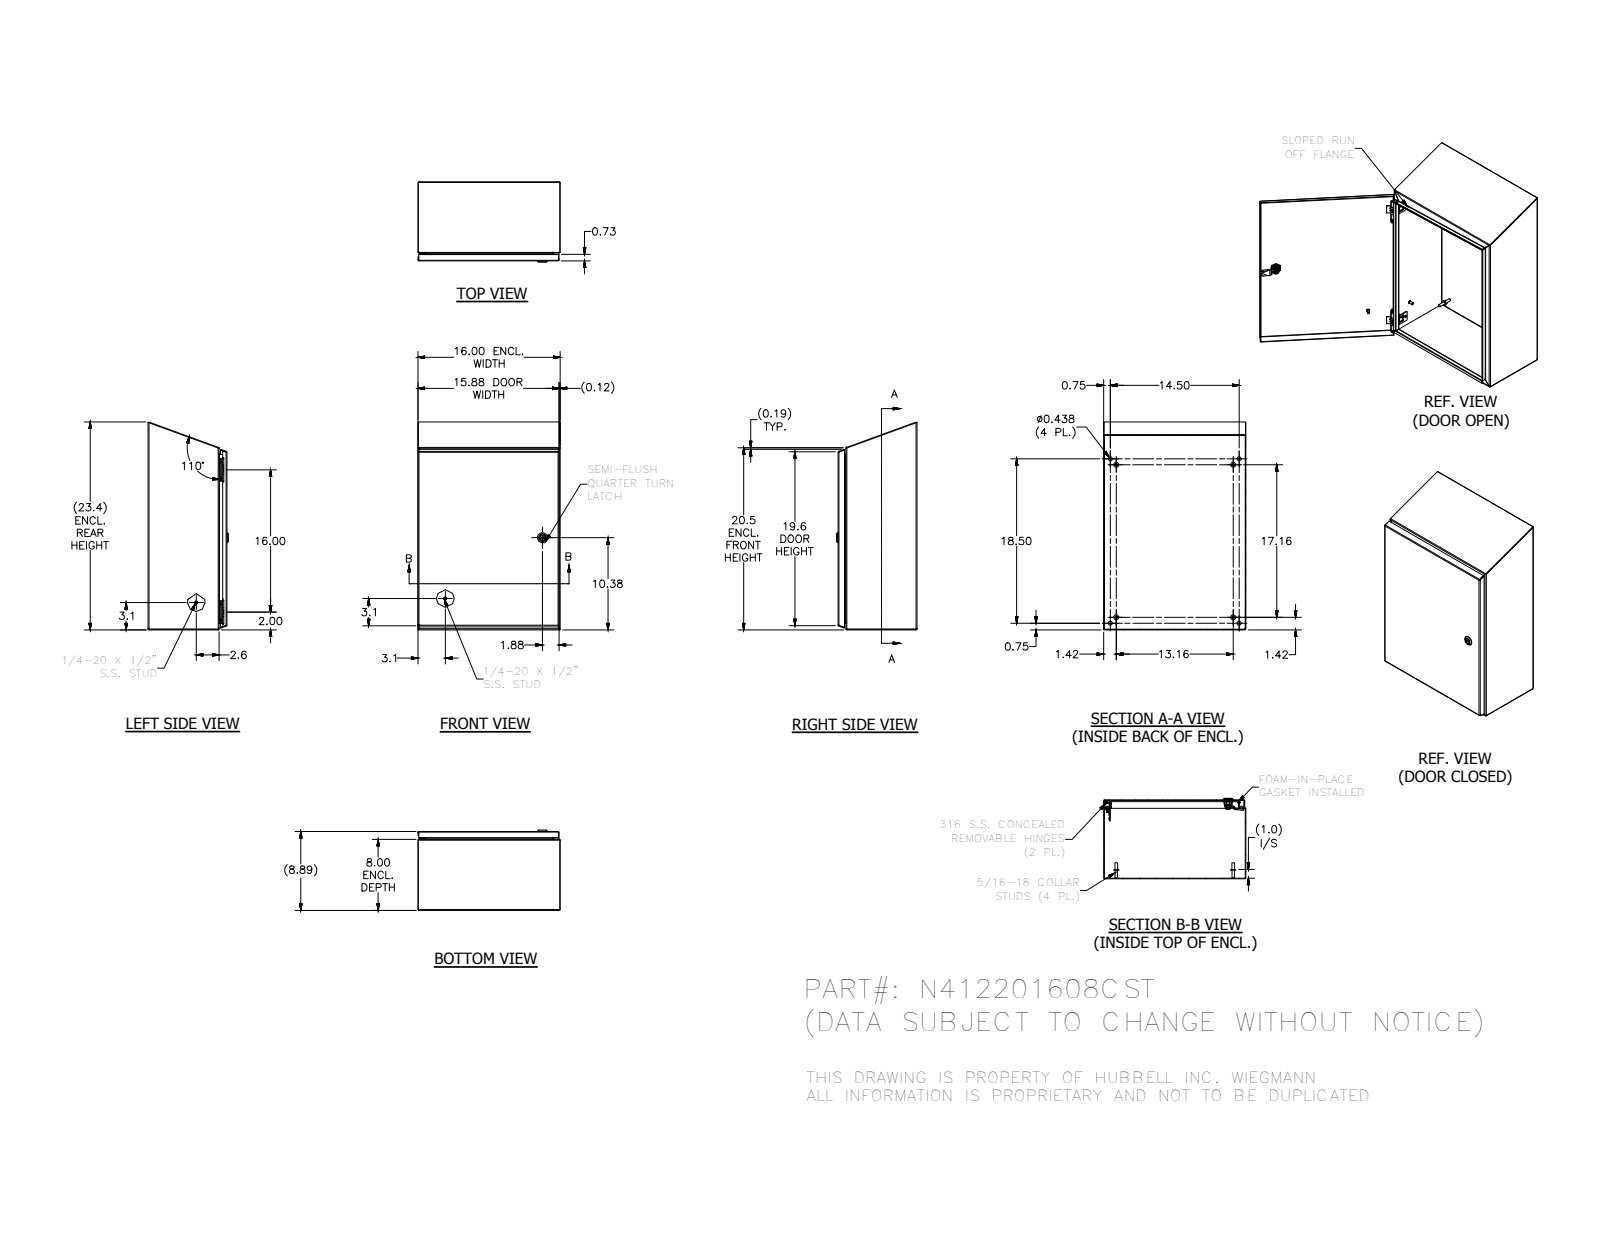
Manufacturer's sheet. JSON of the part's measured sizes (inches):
{"part_name": "N412201608CST", "step_written_by": "SolidWorks 2018 (AUTOMOTIVE_DESIGN)", "units": "inches", "bodies": {"solids": 36, "faces": 1521, "planar": 568, "cylindrical": 552, "other": 401}, "overall_size": [23.391, 16, 9.044], "volume_in3": 108.5, "surface_area_in2": 2952, "round_holes": [[0.093, 4], [0.152, 4], [0.167, 4], [0.172, 4], [0.187, 4], [0.437, 4], [0.156, 3], [0.187, 1], [0.197, 1], [0.315, 1], [0.394, 1], [0.402, 1]], "round_bosses_or_shafts": [[0.25, 10], [0.563, 4], [0.36, 4], [0.32, 4], [0.3, 4], [0.275, 4], [0.256, 4], [0.164, 4]], "partial_cylinders_radius": [[0.012, 30], [0.031, 29], [0.05, 26], [0.105, 19], [0.016, 18], [0.125, 16], [0.02, 13], [0.032, 8]], "face_to_face_distances": [0.074, 8.813, 15.926, 8.739, 8.887, 16, 15.852, 7.926, 0.887, 0.813], "hole_center_spacings": [16, 0.5, 0.656, 0.66, 0.984, 1.307, 1.311, 1.618]}
